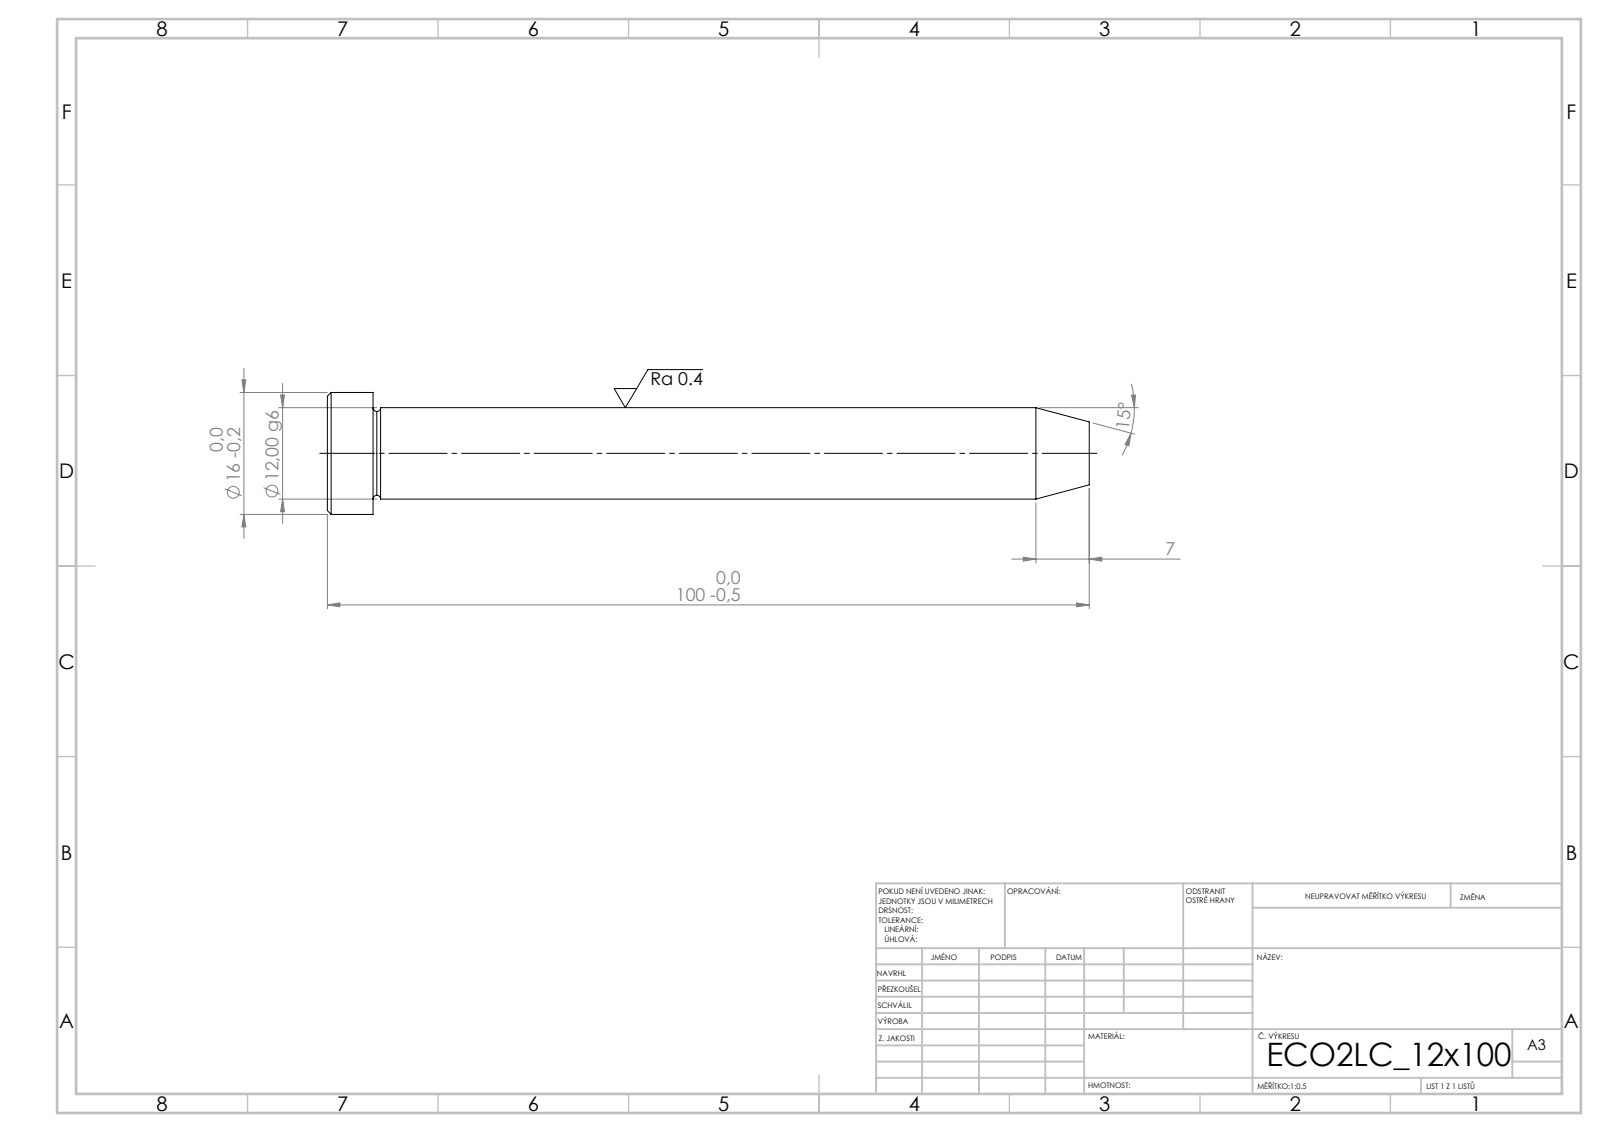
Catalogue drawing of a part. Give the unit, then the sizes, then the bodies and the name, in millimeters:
Units: millimetres
Overall size (bounding box): 100 × 16 × 16
Round bosses / shafts (diameter × count): ⌀16 ×1, ⌀12 ×1
Main face-to-face distances: 6, 94, 100
Volume: 11 595 mm³ · Surface area: 4 158 mm²
Bodies: 1 solid, 15 faces (3 planar, 4 cylindrical, 8 other)
STEP written by: SolidWorks 2019 (CONFIG_CONTROL_DESIGN)
